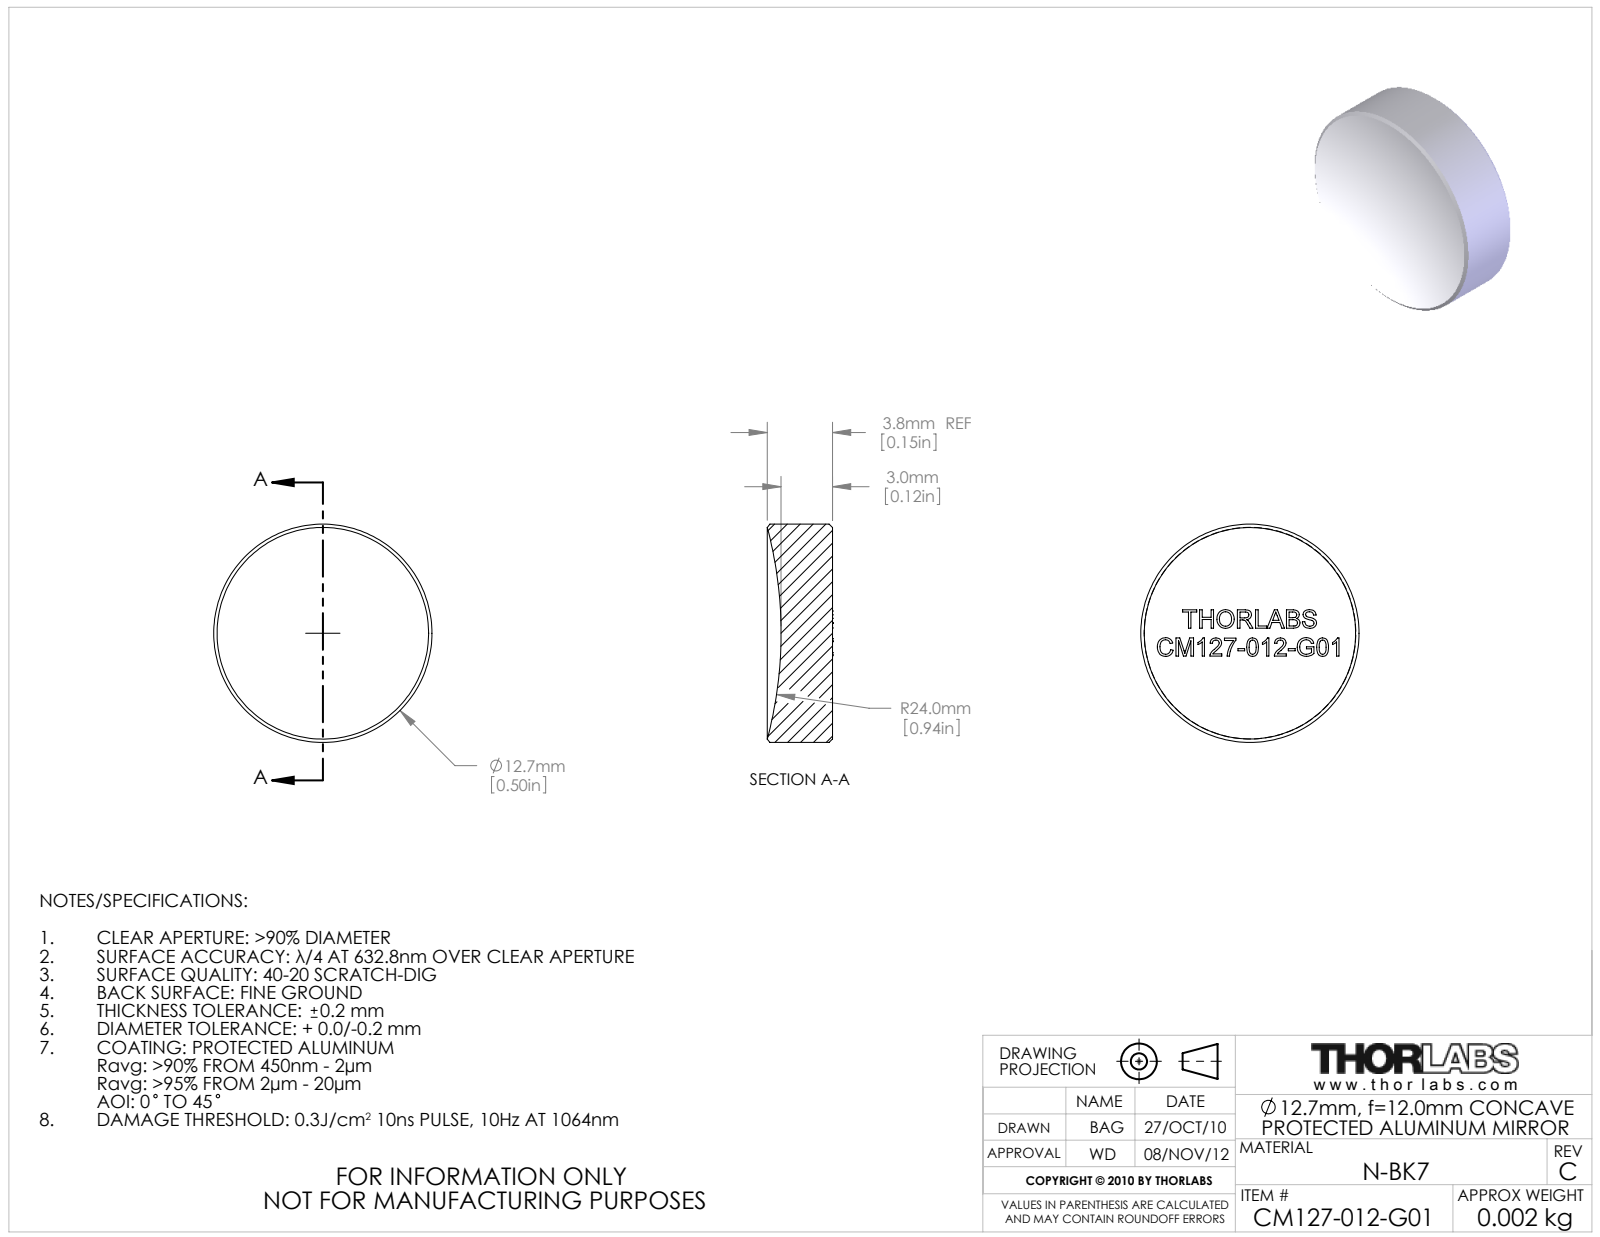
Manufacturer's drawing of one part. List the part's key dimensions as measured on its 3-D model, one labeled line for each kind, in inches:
Part name (STEP PRODUCT): 12006-E0W
STEP written by: SolidWorks 2009 (AUTOMOTIVE_DESIGN)
Units: inches
Bodies: 1 solid, 261 faces (145 planar, 2 cylindrical, 114 other)
Overall size (bounding box): 0.5 × 0.5 × 0.15
Volume: 0.026 in³ · Surface area: 0.618 in²
Round bosses / shafts (diameter × count): ⌀0.5 ×1
Main face-to-face distances: 0.042, 0.052, 0.04, 0.046, 0.037, 0.064, 0.026, 0.173, 0.02, 0.036
